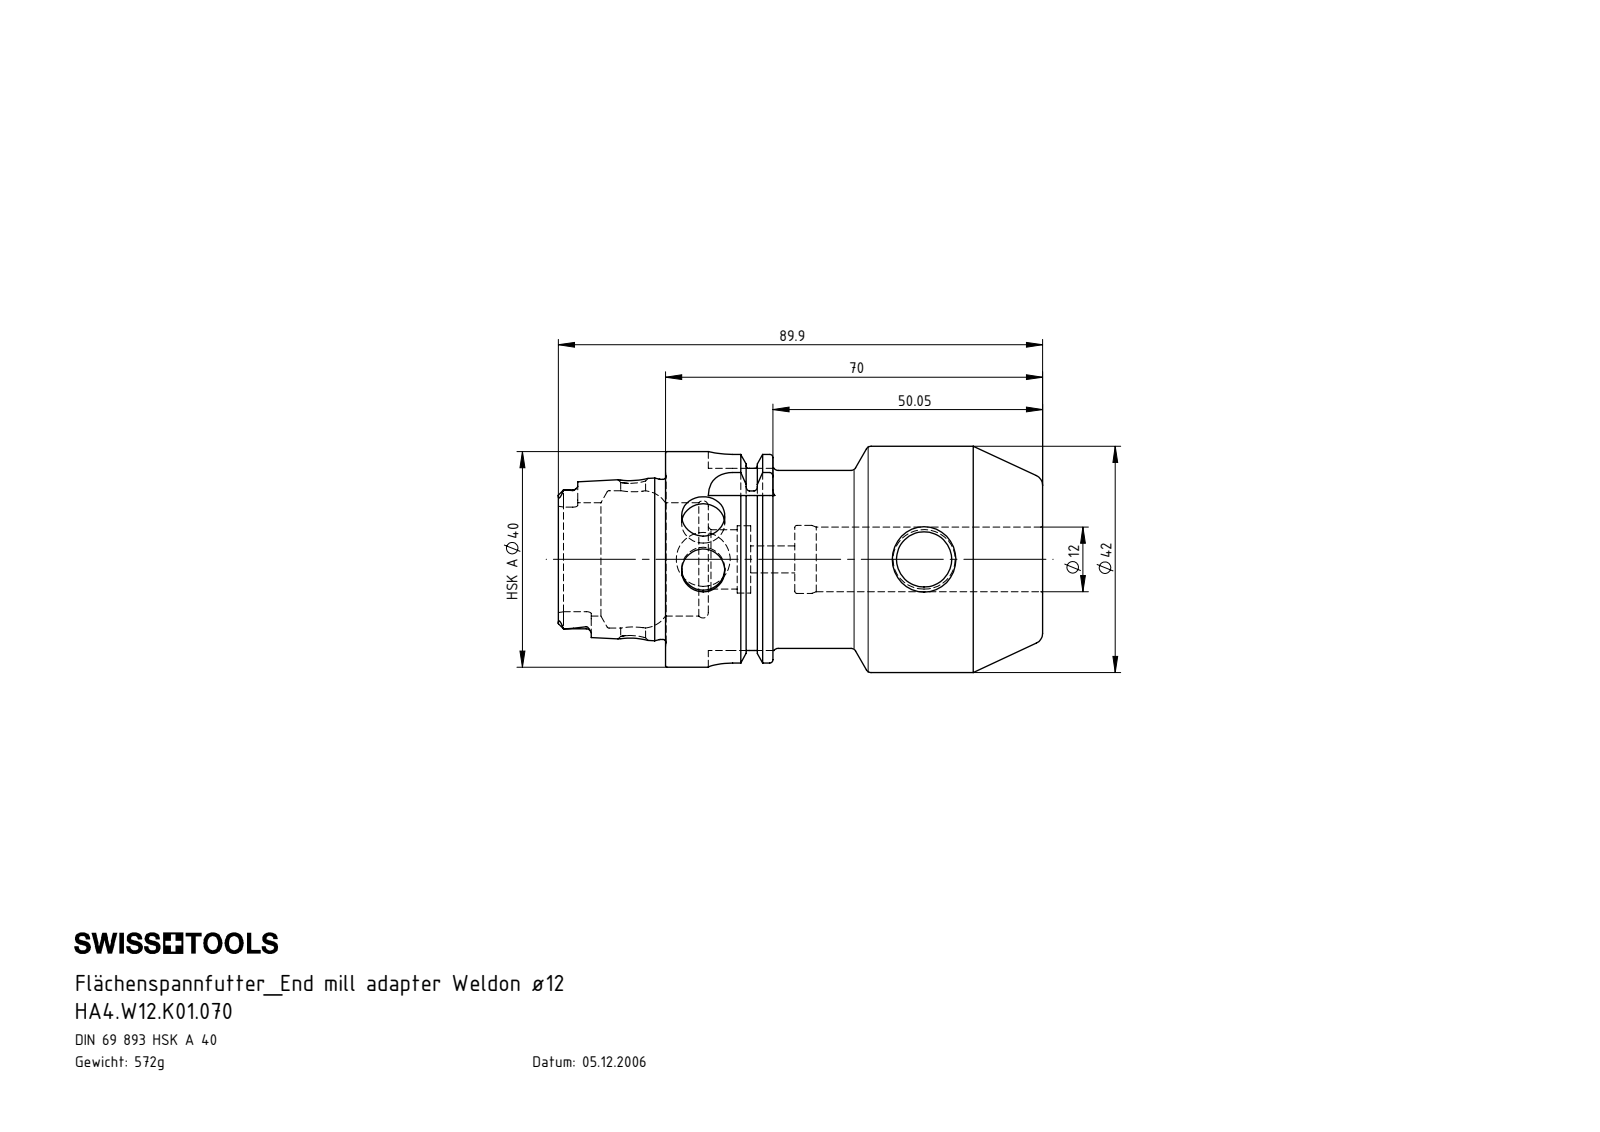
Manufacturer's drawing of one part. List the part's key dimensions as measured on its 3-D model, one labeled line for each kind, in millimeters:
Part name (STEP PRODUCT): HA4-W12.K01.070_B_Fertigbearbeitung; W12-ER1.001.016; HA4.W12.K01.070
STEP written by: SolidWorks 2017 (CONFIG_CONTROL_DESIGN)
Units: millimetres
Bodies: 2 solids, 207 faces (58 planar, 60 cylindrical, 89 other)
Overall size (bounding box): 89.9 × 42 × 42
Volume: 74 231 mm³ · Surface area: 19 004 mm²
Round holes (diameter × count): ⌀8 ×2, ⌀4.6 ×1, ⌀5 ×1, ⌀10 ×1, ⌀10.25 ×1, ⌀11 ×1, ⌀12 ×1, ⌀12.5 ×1, ⌀12.6 ×1, ⌀21 ×1, ⌀25.5 ×1
Round bosses / shafts (diameter × count): ⌀42 ×1, ⌀40 ×1, ⌀34.75 ×1, ⌀33 ×1, ⌀29.71 ×1, ⌀12 ×1
Partial cylindrical surfaces — rounded edges, fillets, slot ends (radius × count): R0.9 ×6, R1.88 ×4, R4.5 ×4
Main face-to-face distances: 70, 7.95, 62.05, 19.95, 12, 50.05, 19.9, 27.85, 39.85, 89.9
Hole centre spacings: 41
